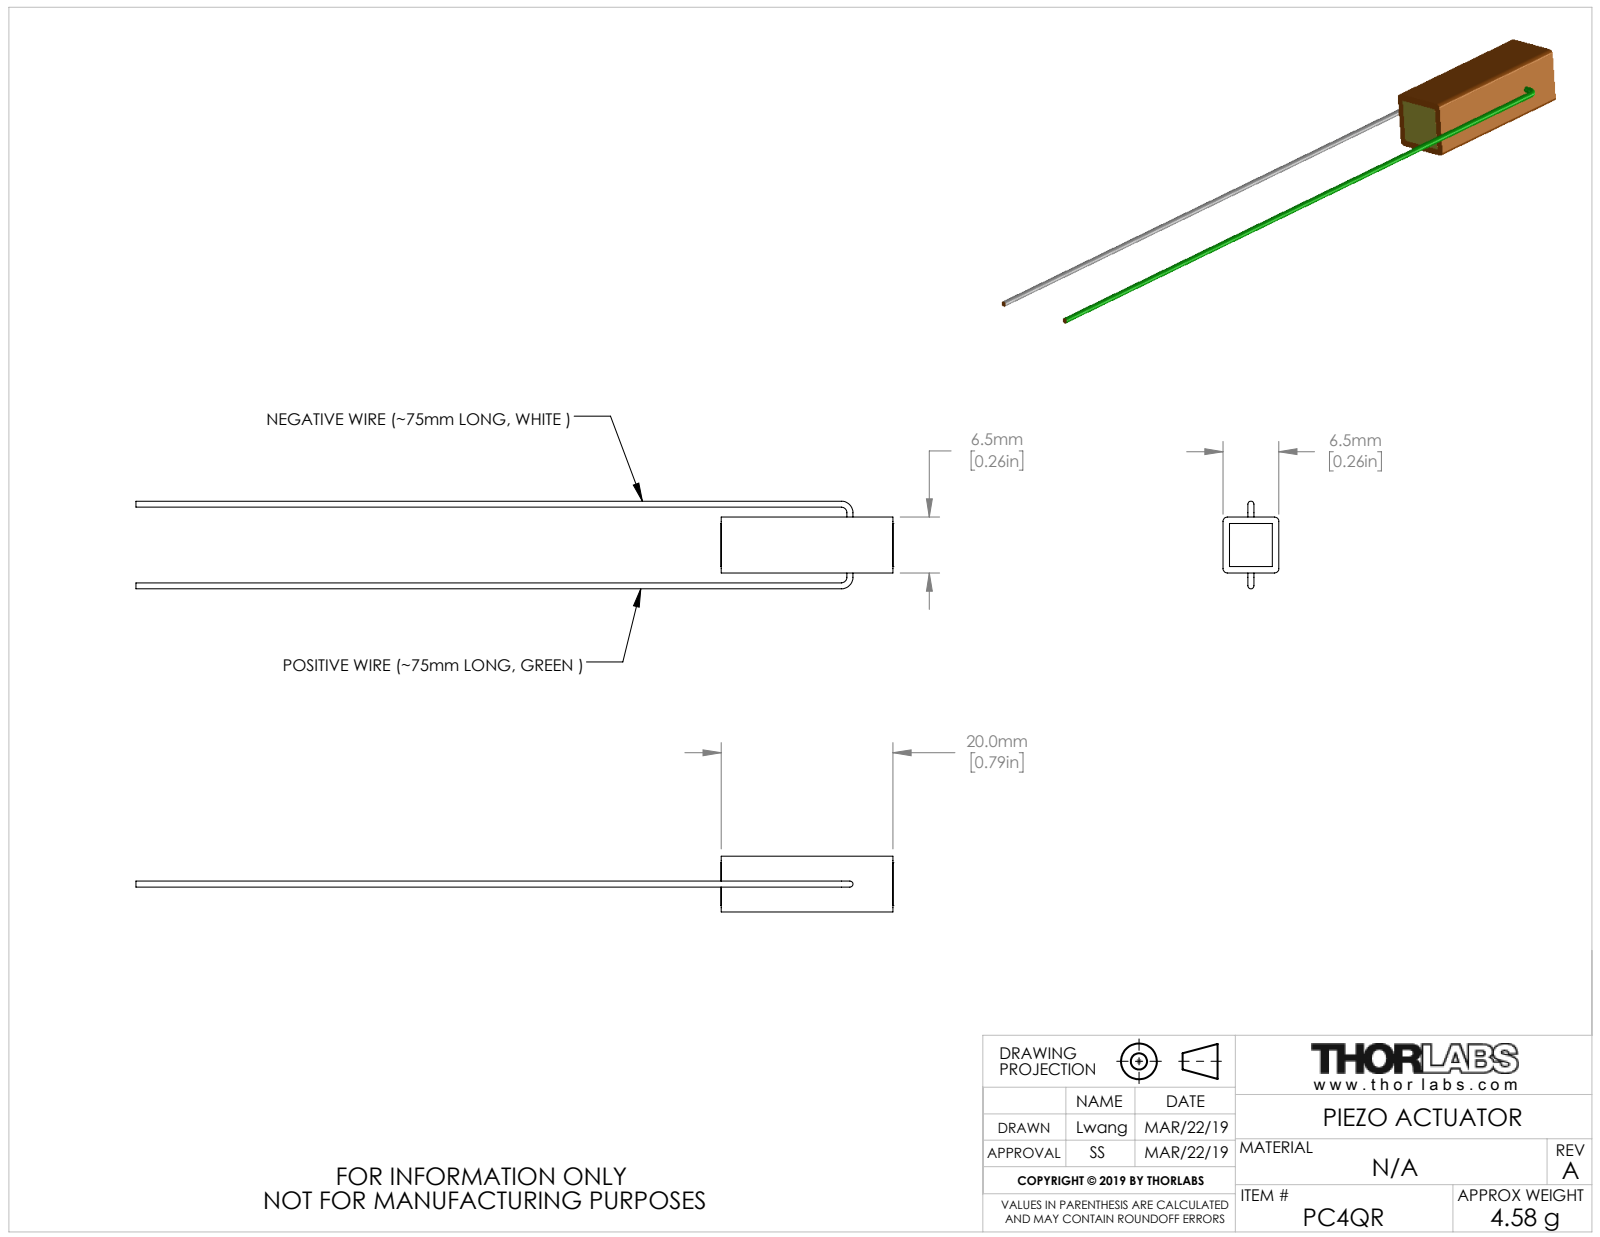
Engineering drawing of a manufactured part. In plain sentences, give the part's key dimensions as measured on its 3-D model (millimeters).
The part is named "CTN013638". Its 3-D file was written by "SolidWorks 2018 (AUTOMOTIVE_DESIGN)". It is 1 solid with 34 faces: 18 planar, 12 cylindrical and 4 other. Overall it measures 88.13 by 10.2 by 6.5 millimeters. Its volume is 906 cubic millimeters and its surface area 958 square millimeters. Round bosses or shafts: 3 of diameter 0.7. Partial cylindrical surfaces (rounded edges, fillets, slot ends): 4 of radius 0.5. The main face-to-face distances are 6.5, 20.01, 20.02, 20, 68.11, 68.12, 88.12, 88.13, 5.75, 0.75.
